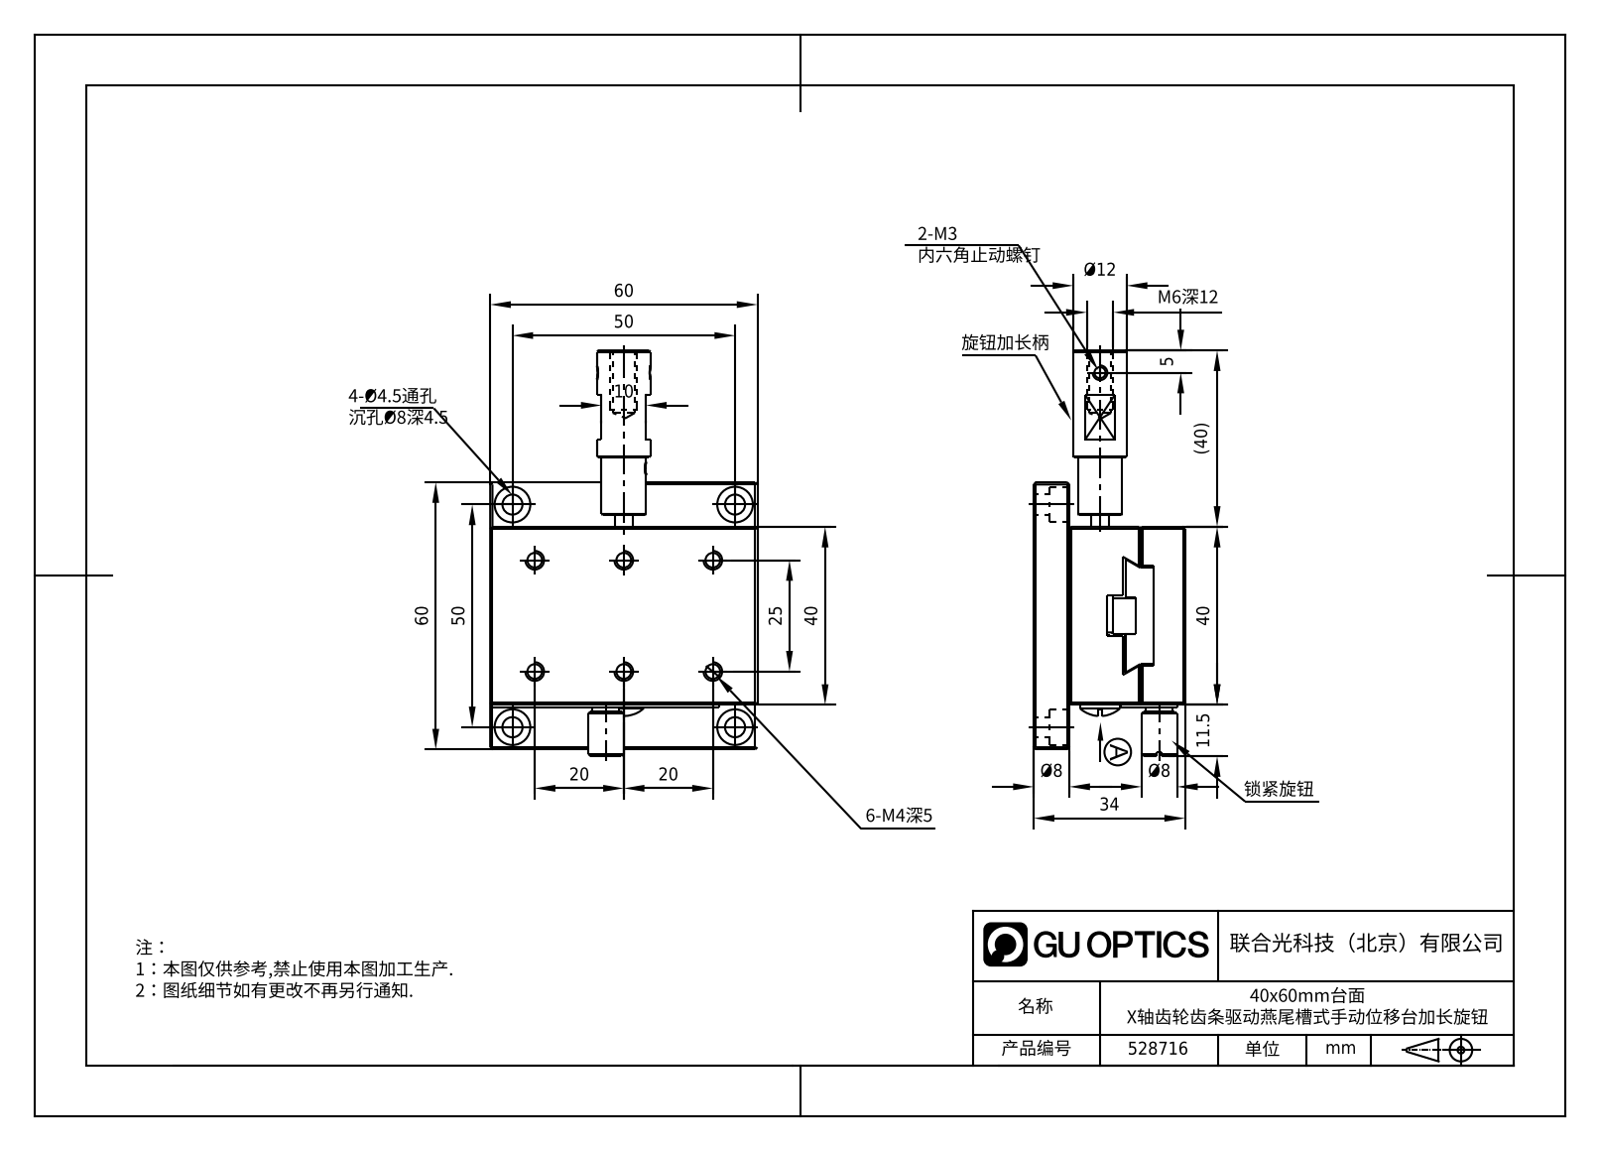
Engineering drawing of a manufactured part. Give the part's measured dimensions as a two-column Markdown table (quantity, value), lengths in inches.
| quantity | value |
| --- | --- |
| part name | 528716 |
| STEP written by | SolidWorks 2020 (CONFIG_CONTROL_DESIGN) |
| units | inches |
| bodies | 0 solids, 295 faces (176 planar, 65 cylindrical, 54 other) |
| overall size | 3.602 × 2.362 × 1.339 |
| round holes (diameter × count) | 0.128 × 8, 0.315 × 6, 0.079 × 4, 0.097 × 4, 0.11 × 4, 0.177 × 4, 0.197 × 4, 0.062 × 2, 0.087 × 2, 0.165 × 2, 0.157 × 1, 0.217 × 1 |
| round bosses / shafts (diameter × count) | 0.315 × 2, 0.472 × 1, 0.394 × 1, 0.354 × 1, 0.256 × 1, 0.236 × 1, 0.23 × 1, 0.138 × 1 |
| partial cylindrical surfaces (radius × count) | 0.079 × 4, 0.071 × 2 |
| main face-to-face distances | 0.315, 0.276, 0.748, 1.339, 1.024, 1.063, 0.394, 0.63, 0.945, 0.02 |
| hole center spacings | 1.1, 1.774, 0.506, 0.53, 0.546, 0.574, 0.696, 0.787 |
